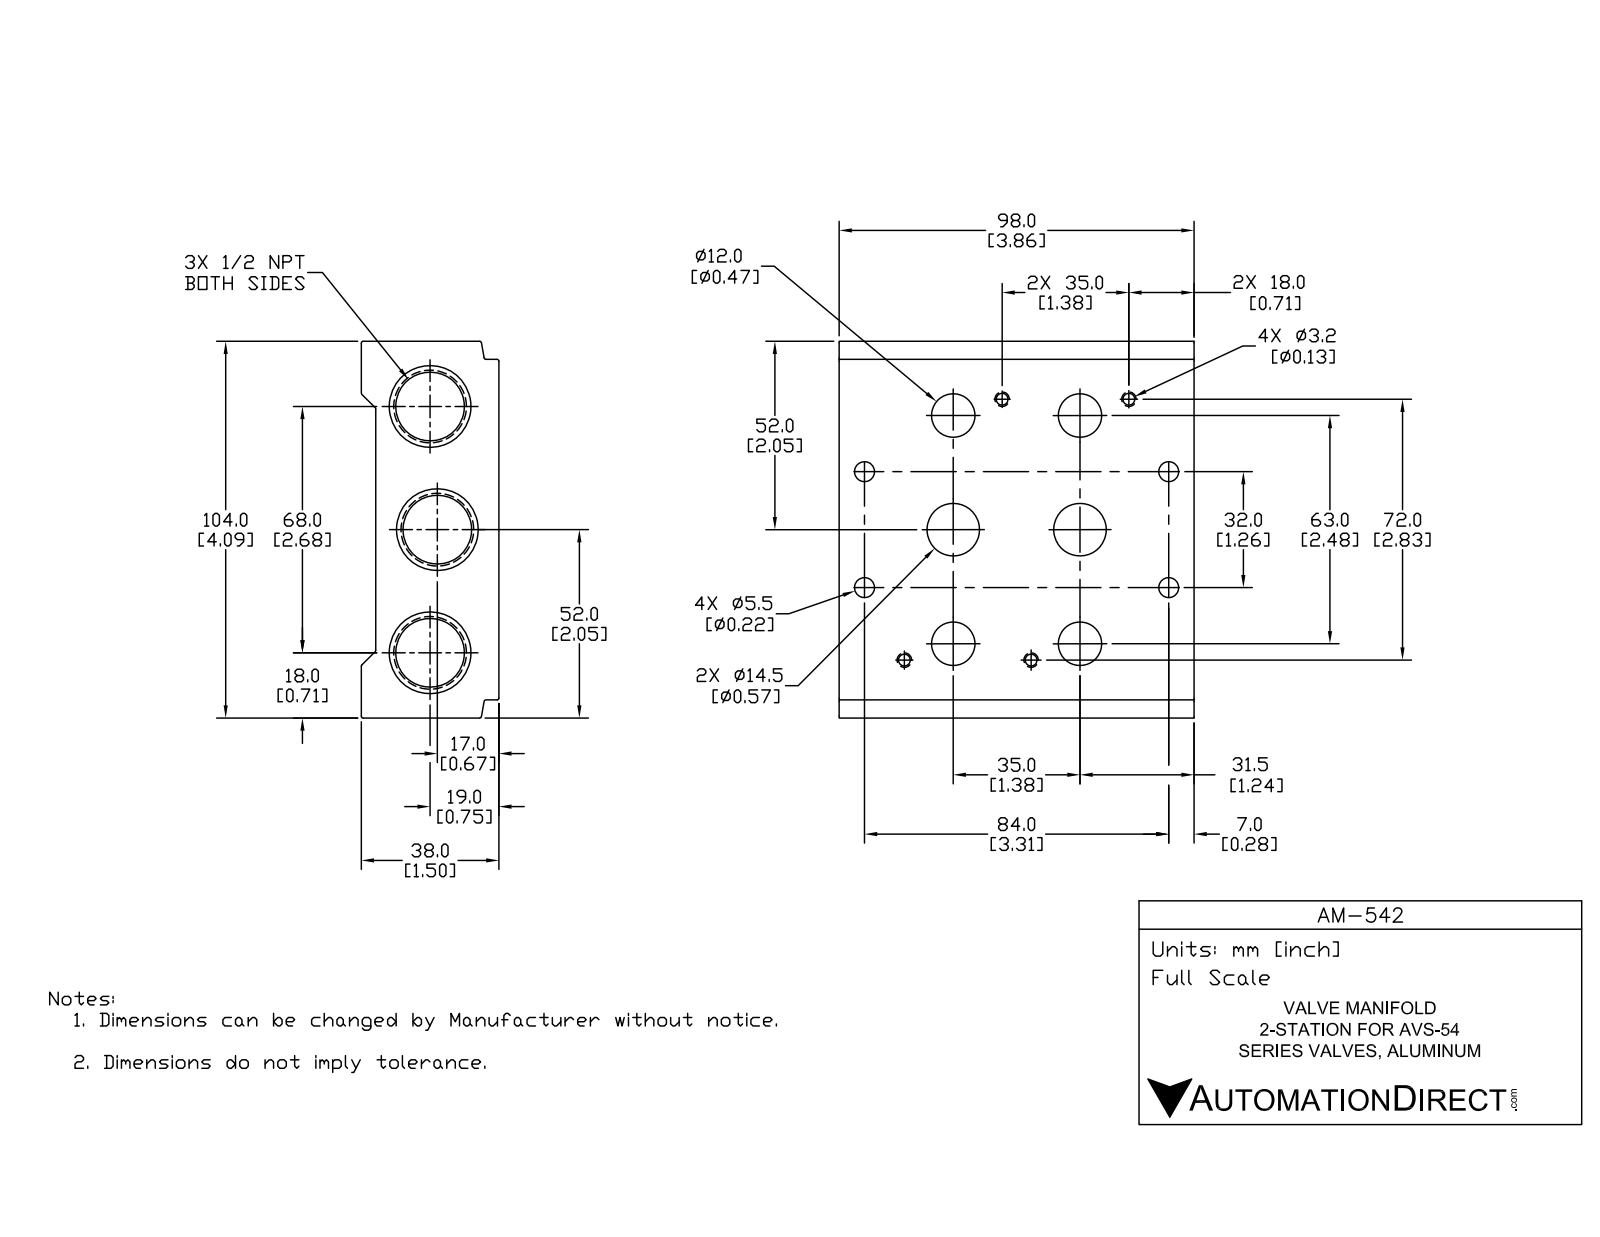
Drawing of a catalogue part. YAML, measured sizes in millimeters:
part_name: "AM-542"
step_written_by: "SolidWorks 2015 (CONFIG_CONTROL_DESIGN)"
units: millimeters
bodies: {solids: 1, faces: 93, planar: 28, cylindrical: 45, other: 20}
overall_size: [104, 98, 38]
volume: 275431
surface_area: 54617
round_holes:
  - {diameter: 3.3, count: 4}
  - {diameter: 5.5, count: 4}
  - {diameter: 8.5, count: 4}
  - {diameter: 17.86, count: 3}
  - {diameter: 13, count: 2}
partial_cylinders:
  - {radius: 0.5, count: 11}
face_to_face_distances: [38, 4, 34, 104, 98, 13.57, 84.43, 28, 24, 10]
hole_center_spacings: [35, 14.23, 28.99, 29.26, 31.5, 38.45, 47.09, 53.45]
